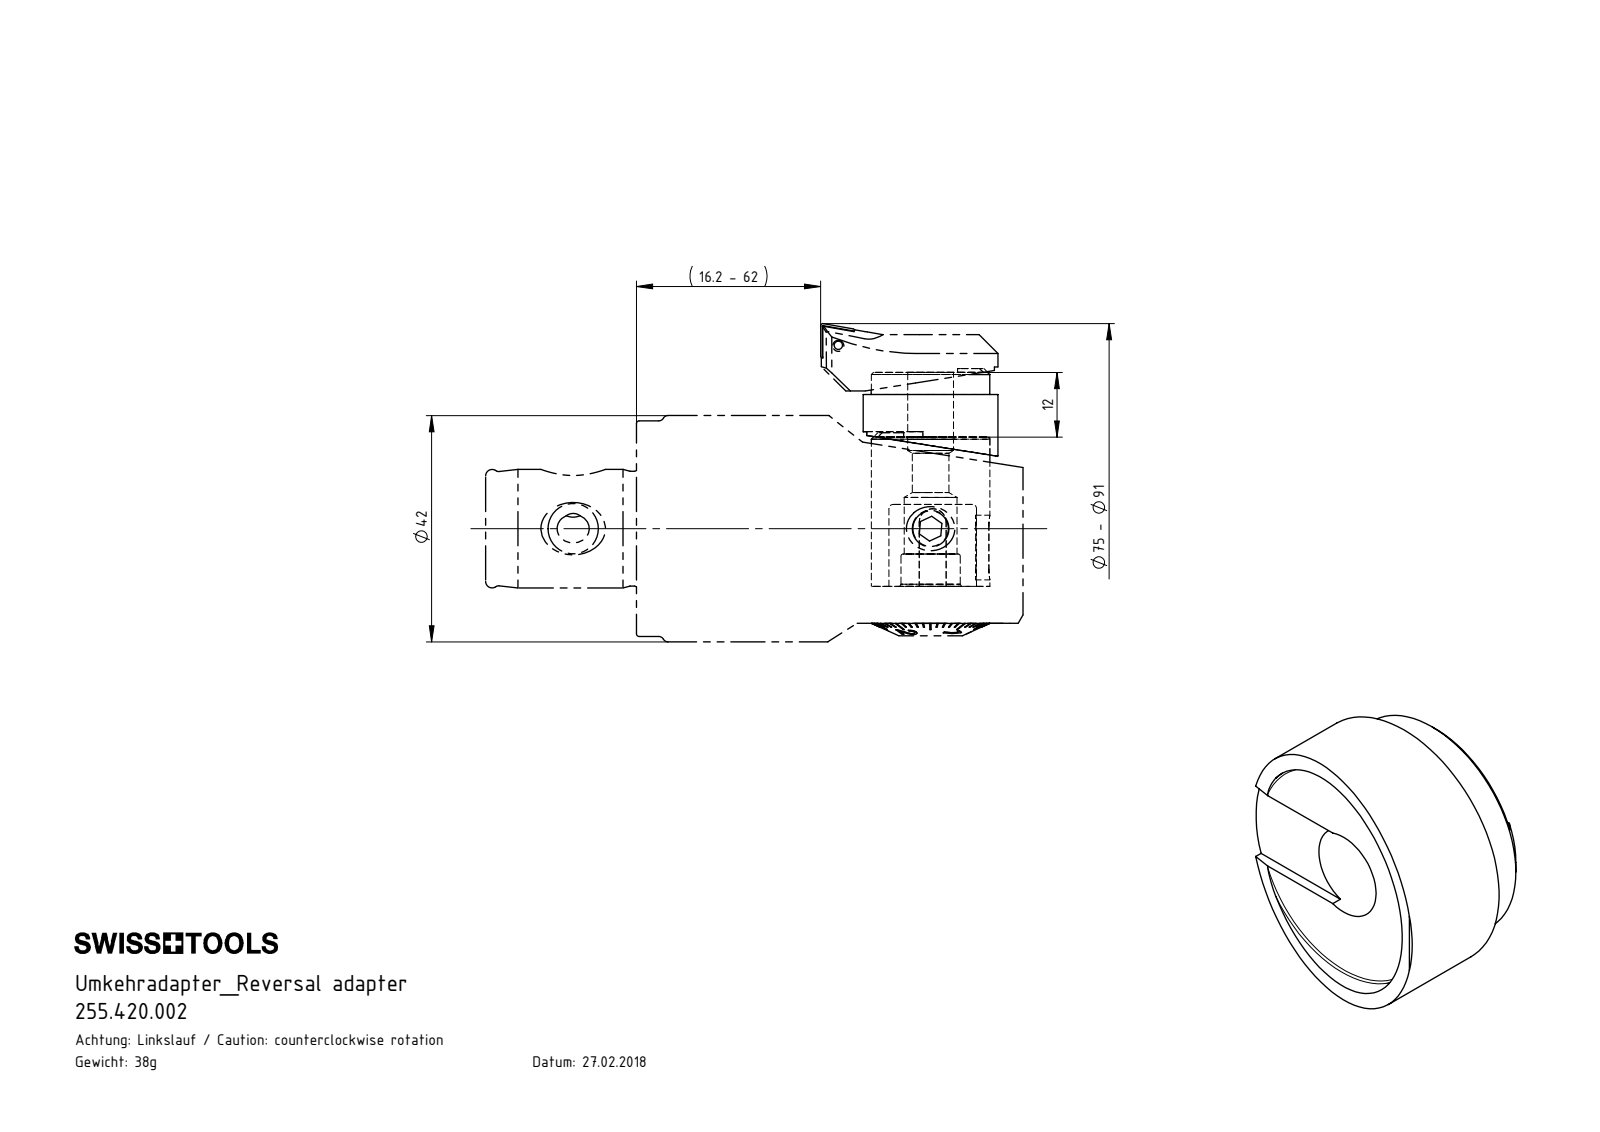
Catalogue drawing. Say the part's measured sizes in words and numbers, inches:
The part is named "255.420.002; F42-U00.001.012_B". Its 3-D file was written by "SolidWorks 2017 (CONFIG_CONTROL_DESIGN)". It is 1 solid with 28 faces: 12 planar, 11 cylindrical and 5 other. Overall it measures 0.984 by 0.984 by 0.638 inches. Its volume is 0.298 cubic inches and its surface area 3.604 square inches. Round holes: 1 of diameter 0.335, 1 of diameter 0.866. Round bosses or shafts: 1 of diameter 0.984. Partial cylindrical surfaces (rounded edges, fillets, slot ends): 2 of radius 0.02. The main face-to-face distances are 0.472, 0.161, 0.311, 0.433, 0.272, 0.039, 0.028, 0.189, 0.461, 0.5.
